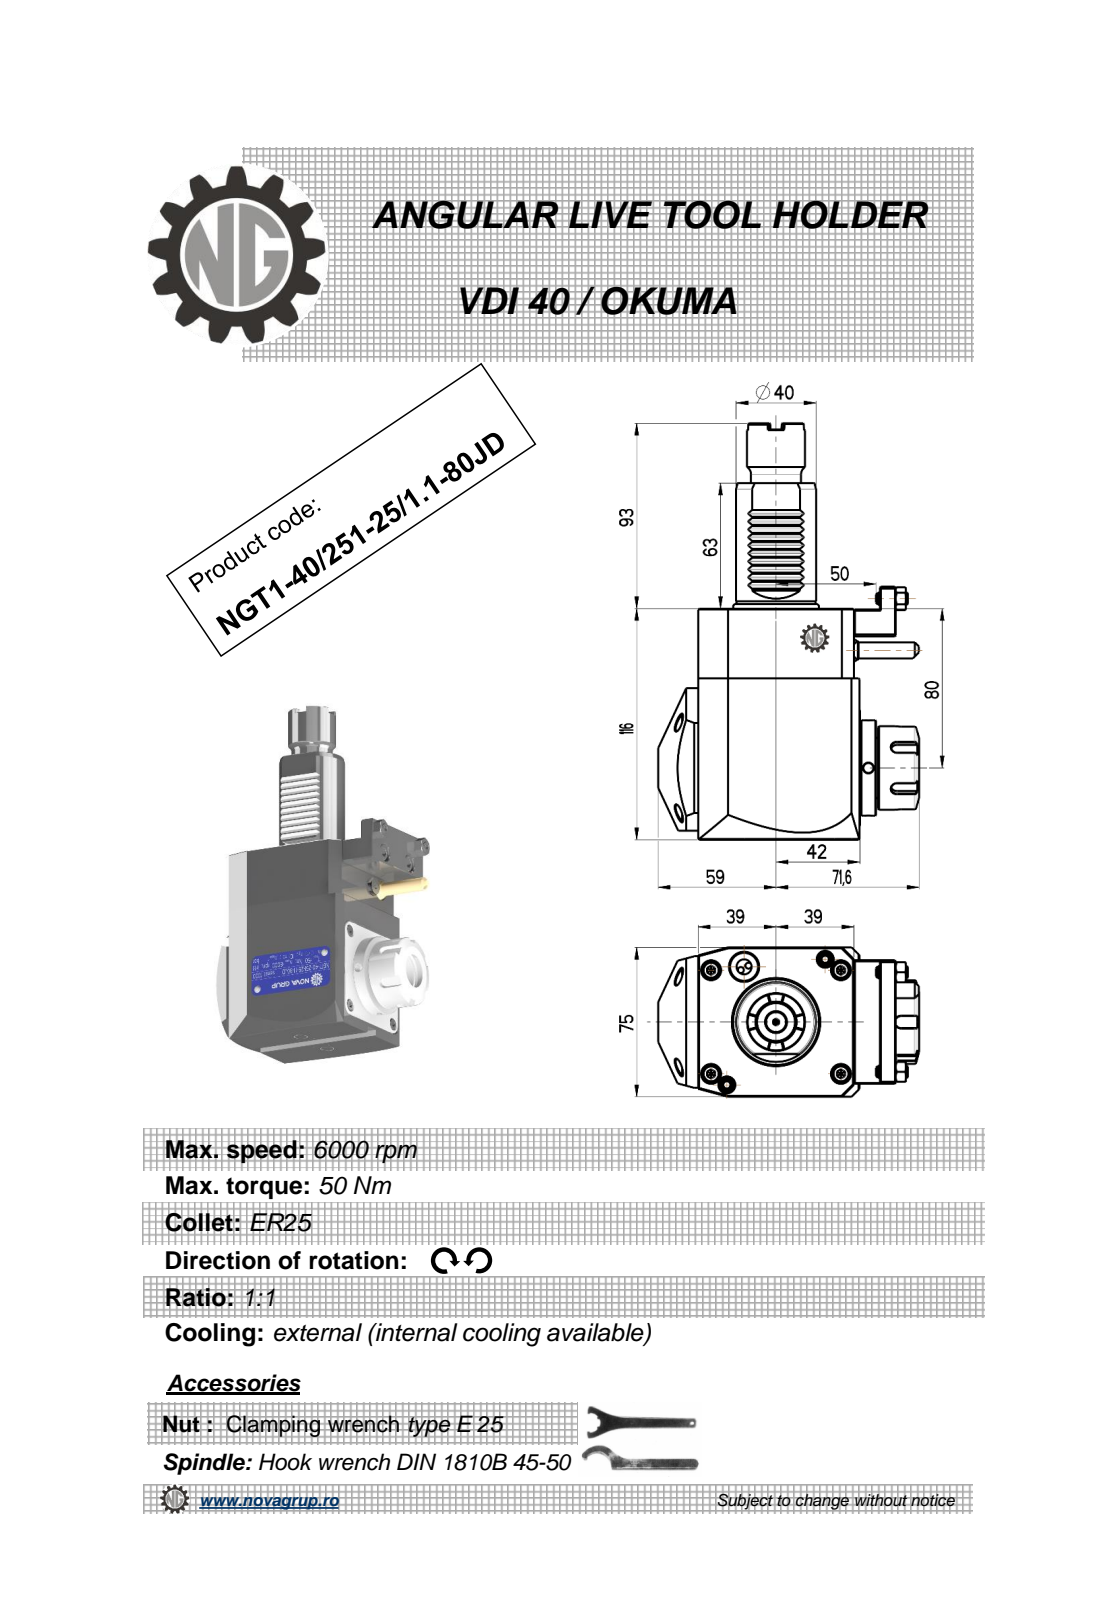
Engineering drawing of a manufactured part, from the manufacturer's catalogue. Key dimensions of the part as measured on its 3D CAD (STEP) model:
Part name (STEP PRODUCT): NGT1_40_251_25_1_1_80JD
STEP written by: PRO/ENGINEER BY PARAMETRIC TECHNOLOGY CORPORATION, 2010280 (CONFIG_CONTROL_DESIGN)
Units: millimetres
Bodies: 1 solid, 479 faces (196 planar, 86 cylindrical, 197 other)
Overall size (bounding box): 209 × 130.6 × 76.6
Volume: 894 216 mm³ · Surface area: 74 118 mm²
Round holes (diameter × count): ⌀5 ×3, ⌀3 ×1, ⌀20.3 ×1
Round bosses / shafts (diameter × count): ⌀6 ×2, ⌀48 ×1, ⌀42 ×1, ⌀40 ×1, ⌀37.5 ×1, ⌀33 ×1, ⌀29 ×1, ⌀25 ×1
Partial cylindrical surfaces — rounded edges, fillets, slot ends (radius × count): R0.3 ×10, R0.31 ×10, R0.2 ×6, R3 ×5, R0.5 ×1, R10 ×1, R40 ×1
Main face-to-face distances: 75, 116, 81, 0.5, 10, 21, 11, 80.8, 8, 18
Hole centre spacings: 61.13
